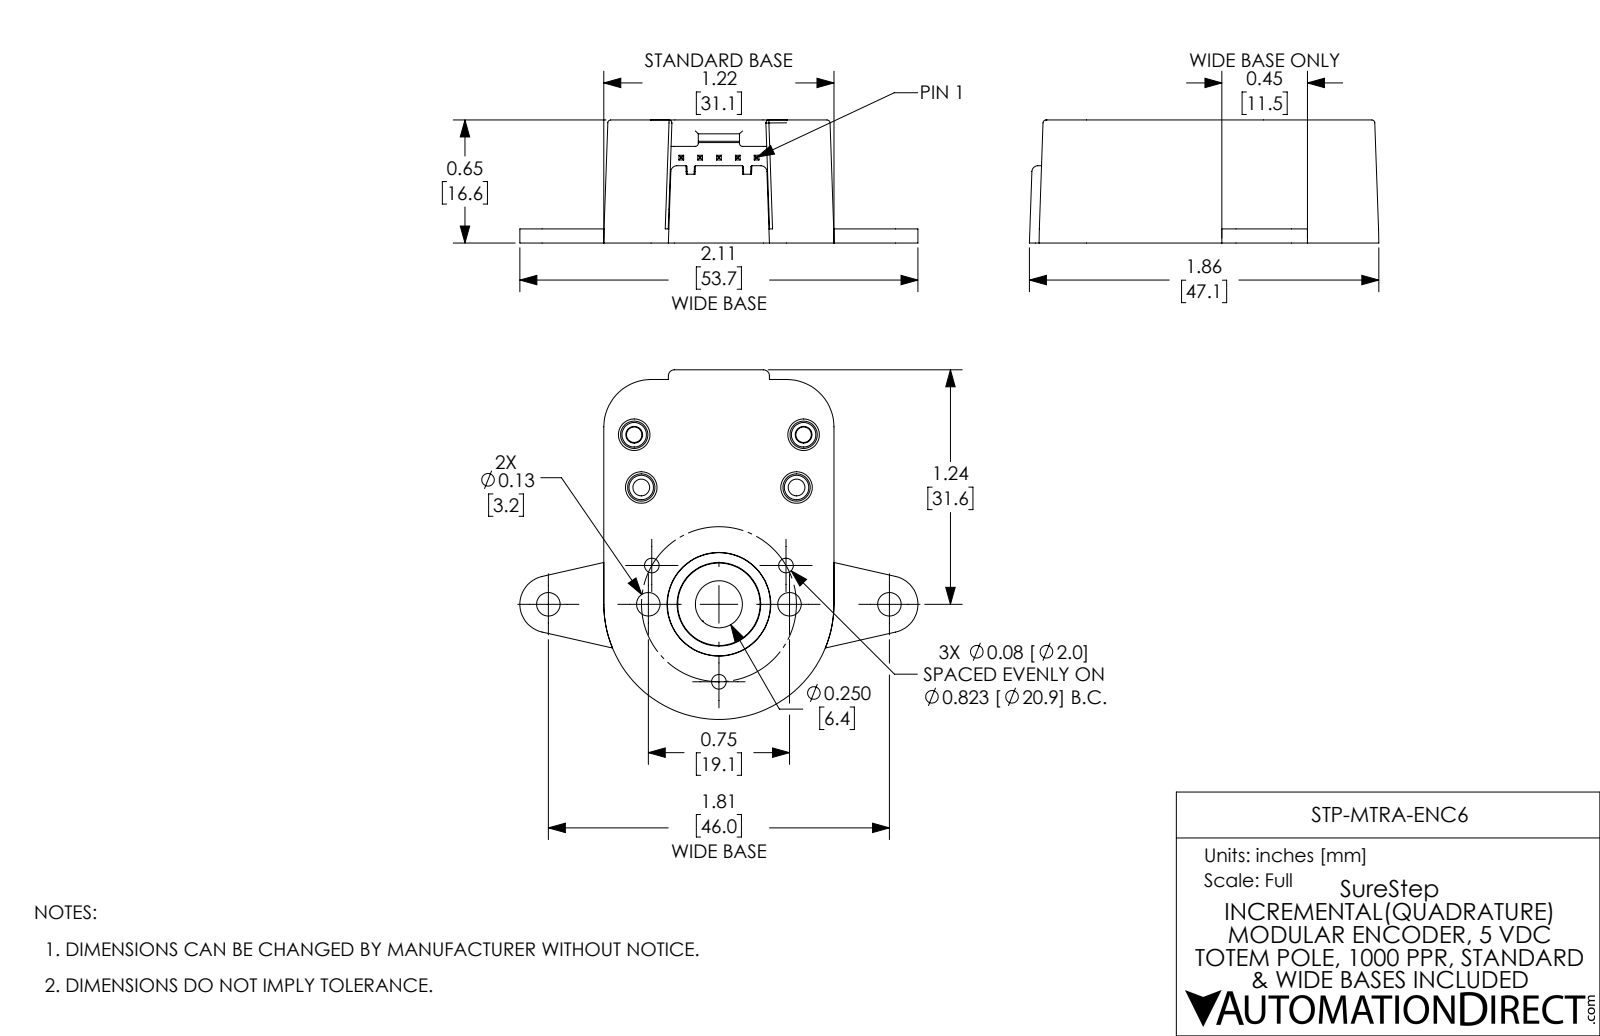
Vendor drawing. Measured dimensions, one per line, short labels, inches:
name: STP-MTRA-ENC6
written by: SolidWorks 2017 (AUTOMOTIVE_DESIGN)
unit: in
bodies: 14 solids, 1349 faces (481 planar, 334 cylindrical, 534 other)
size: 3.75 × 1.865 × 0.671
volume: 0.489 in³; area: 25.74 in²
holes: 6× ⌀0.078, 6× ⌀0.145, 5× ⌀0.125, 4× ⌀0.089, 2× ⌀0.095, 2× ⌀0.109, 2× ⌀0.145, 1× ⌀0.093, 1× ⌀0.125, 1× ⌀0.25, 1× ⌀0.551
bosses: 4× ⌀0.187, 4× ⌀0.16, 4× ⌀0.096, 3× ⌀0.112, 2× ⌀0.195, 1× ⌀0.52, 1× ⌀0.487, 1× ⌀0.375
rounds: 36× R0.016, 34× R0.031, 4× R0.01, 2× R0.047, 2× R0.047, 2× R0.048, 2× R0.075, 2× R0.095
face distances: 0.019, 0.135, 0.653, 0.671, 0.154, 0.518, 0.536, 0.405, 0.117, 0.423
hole spacings: 2.081, 0.207, 0.282, 0.418, 0.557, 0.621, 0.7, 0.713
